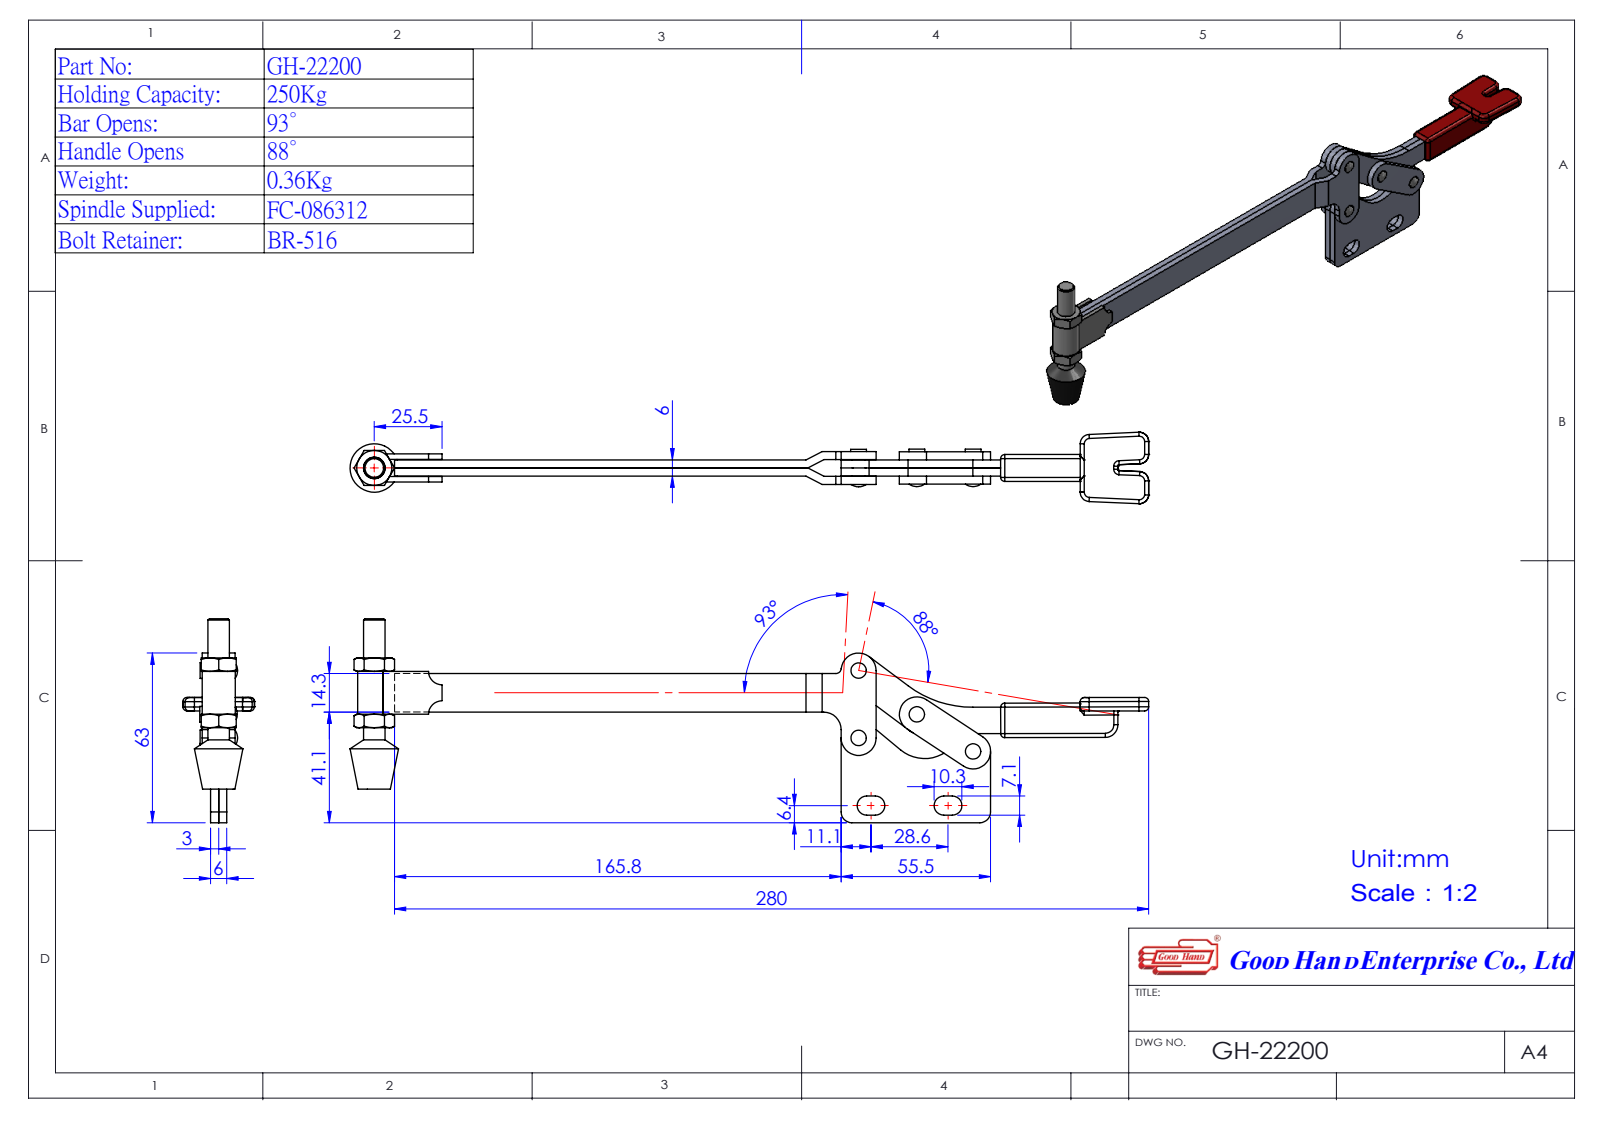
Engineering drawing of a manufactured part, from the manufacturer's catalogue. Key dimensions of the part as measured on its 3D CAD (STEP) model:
Part name (STEP PRODUCT): Group1^GH-22170(簡化); Group2^GH-22180(簡化); Group2^GH-22200(簡化); GH-22200(簡化) (+2 more)
STEP written by: SolidWorks 2016 (AUTOMOTIVE_DESIGN)
Units: millimetres
Bodies: 6 solids, 270 faces (128 planar, 104 cylindrical, 38 other)
Overall size (bounding box): 295.3 × 70.95 × 26.54
Volume: 50 661 mm³ · Surface area: 33 727 mm²
Round holes (diameter × count): ⌀3.5 ×4, ⌀4.83 ×2
Round bosses / shafts (diameter × count): ⌀5.85 ×4, ⌀13 ×1, ⌀7.93 ×1
Partial cylindrical surfaces — rounded edges, fillets, slot ends (radius × count): R3.47 ×6, R3.55 ×4, R6.5 ×4, R0.53 ×2, R2.42 ×2, R4 ×2, R2 ×1, R4.15 ×1
Main face-to-face distances: 3, 6, 3.1, 6.1, 9.1, 9.2, 5, 2.9, 6.2, 2
Hole centre spacings: 25, 23.34, 27.05, 42.79, 52.02
